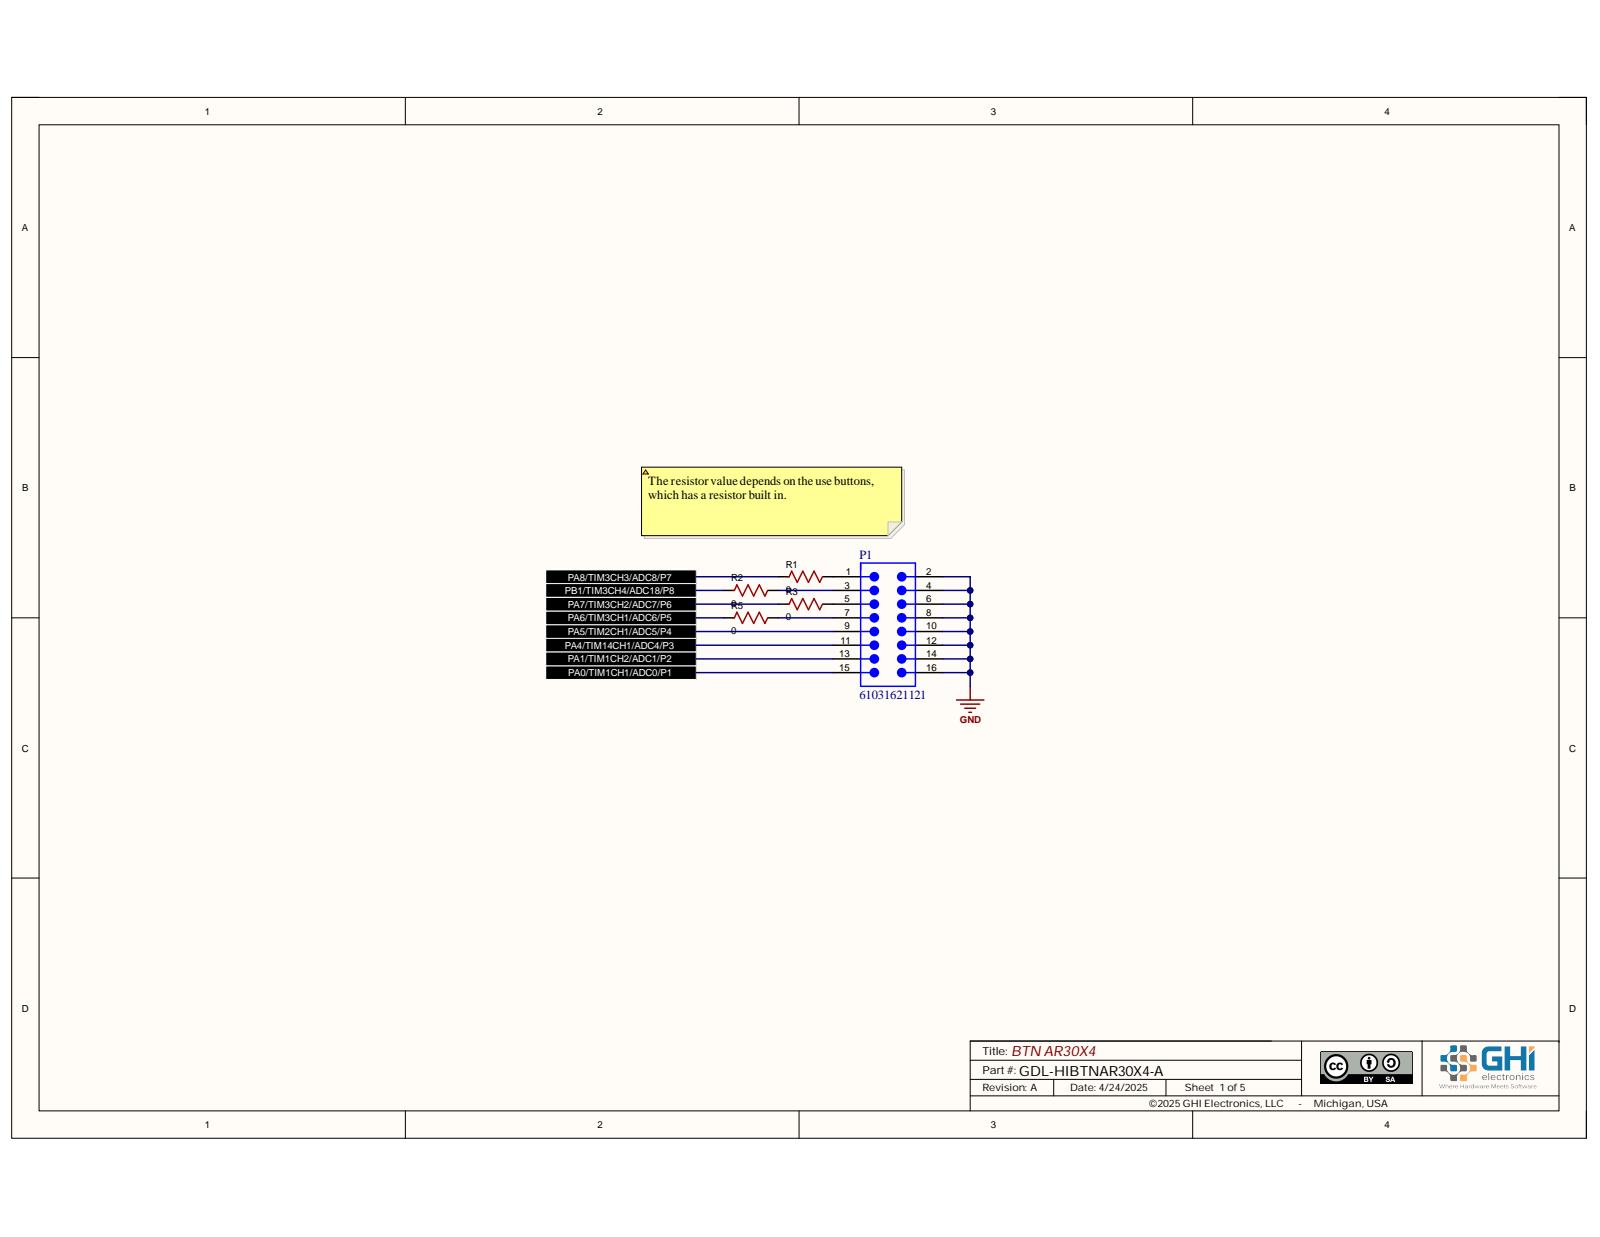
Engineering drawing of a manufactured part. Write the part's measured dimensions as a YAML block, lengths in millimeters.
part_name: "PCB; Board; R5; User Library-R SMD 0402 (+7 more)"
step_written_by: "Open CASCADE 7.5 (AUTOMOTIVE_DESIGN)"
units: millimeters
bodies: {solids: 117, faces: 2147, planar: 1712, cylindrical: 260, other: 175}
overall_size: [92, 92, 26.9]
volume: 59966
surface_area: 29687
round_holes:
  - {diameter: 0.8, count: 4}
  - {diameter: 3, count: 4}
  - {diameter: 25, count: 4}
  - {diameter: 30, count: 4}
  - {diameter: 1.02, count: 2}
round_bosses_or_shafts:
  - {diameter: 29.9, count: 4}
  - {diameter: 24.7, count: 4}
partial_cylinders:
  - {radius: 0.12, count: 35}
  - {radius: 0.15, count: 14}
  - {radius: 3.5, count: 4}
  - {radius: 0.17, count: 2}
  - {radius: 0.18, count: 2}
  - {radius: 0.18, count: 2}
  - {radius: 0.5, count: 2}
  - {radius: 1.14, count: 2}
face_to_face_distances: [1.6, 9.6, 8, 7.15, 8.75, 16.75, 20, 3.25, 10.4, 12]
hole_center_spacings: [68.34, 46, 27.58, 85, 92.63, 6.8, 65.05, 120.21]
